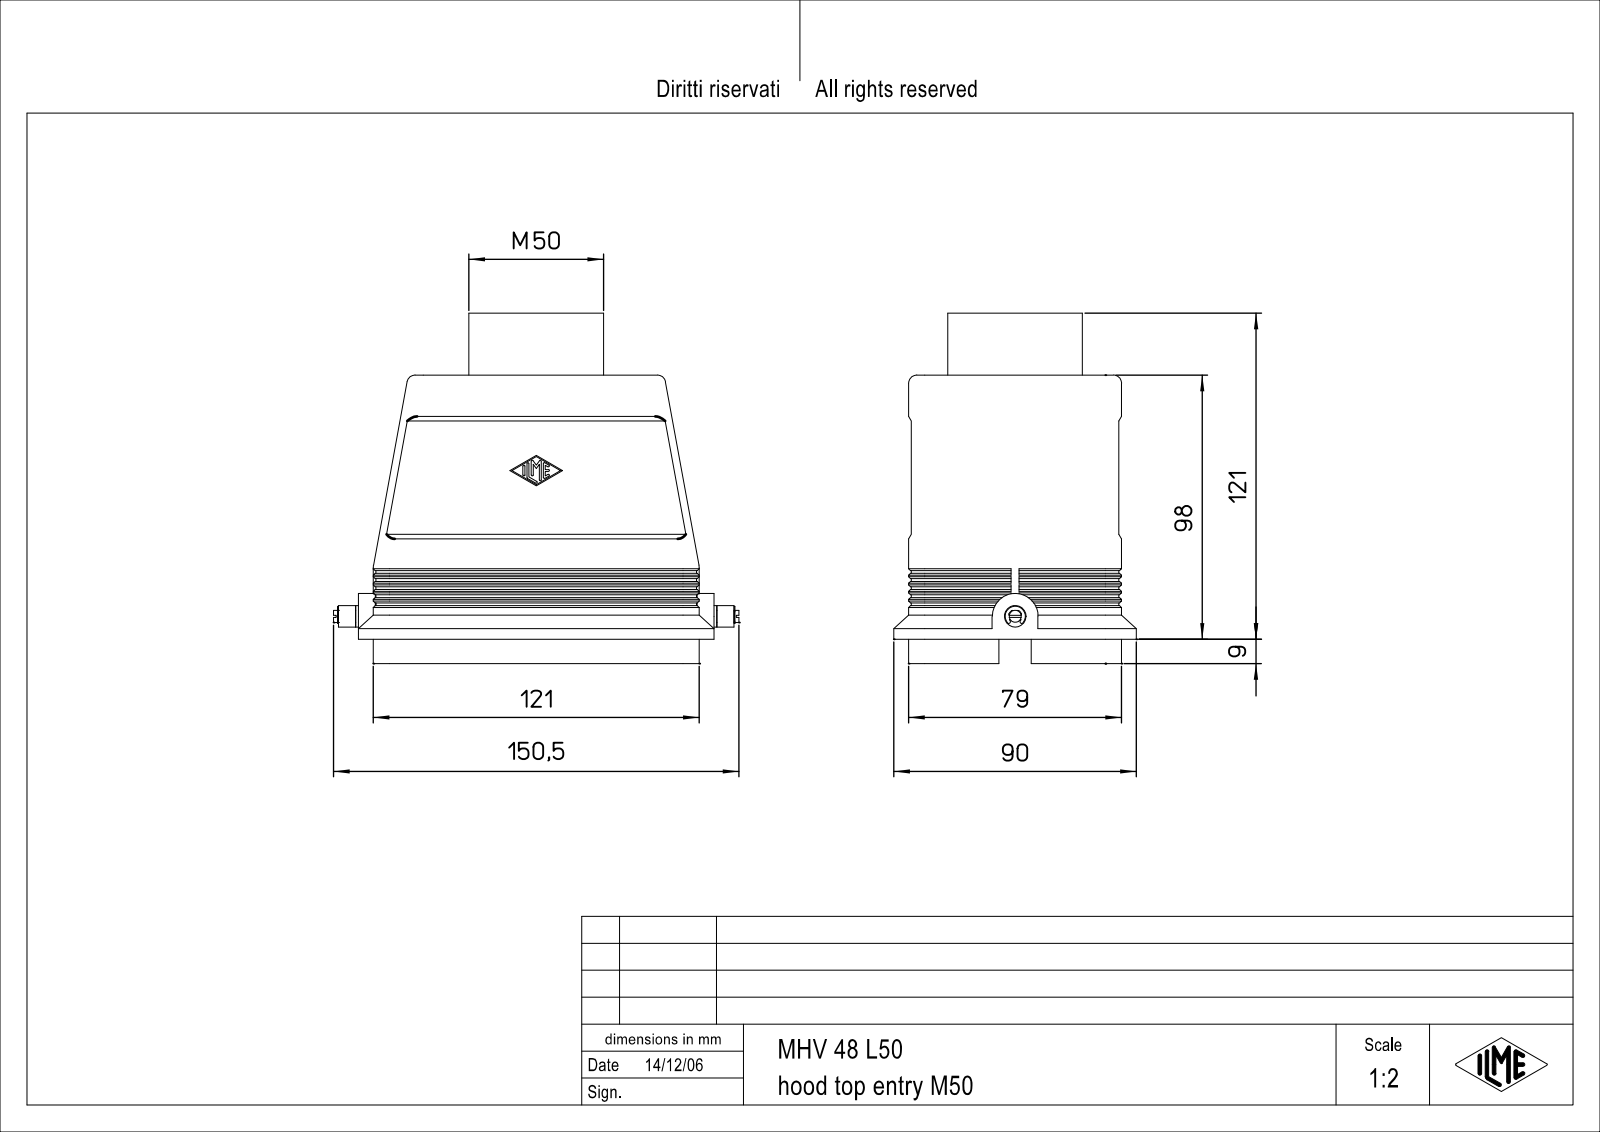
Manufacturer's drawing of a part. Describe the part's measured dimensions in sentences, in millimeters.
The part is named "CH_MH Tüllengehäuse Verschluss für 1 Bügel 104_62 Teil 2". Its 3-D file was written by "Autodesk Inventor 7 (AUTOMOTIVE_DESIGN)". It is 1 solid with 686 faces: 250 planar, 185 cylindrical and 251 other. Overall it measures 150.5 by 127 by 90 millimeters. Its volume is 229 346 cubic millimeters and its surface area 111 056 square millimeters. Round holes: 4 of diameter 2.46, 4 of diameter 3.5, 1 of diameter 48, 1 of diameter 50, 1 of diameter 62. Round bosses or shafts: 1 of diameter 61, 1 of diameter 55, 1 of diameter 53, 1 of diameter 8, 1 of diameter 6, 1 of diameter 4.5, 1 of diameter 3.5. Partial cylindrical surfaces (rounded edges, fillets, slot ends): 14 of radius 0.38, 12 of radius 2, 10 of radius 6, 4 of radius 0.5, 4 of radius 3, 4 of radius 11.5, 3 of radius 0.95, 2 of radius 0.62. The main face-to-face distances are 3.5, 72, 75.5, 1, 109, 2.5, 79, 74.5, 78, 10. The hole center spacings are 27, 52.15, 60.54, 104, 107.45.
